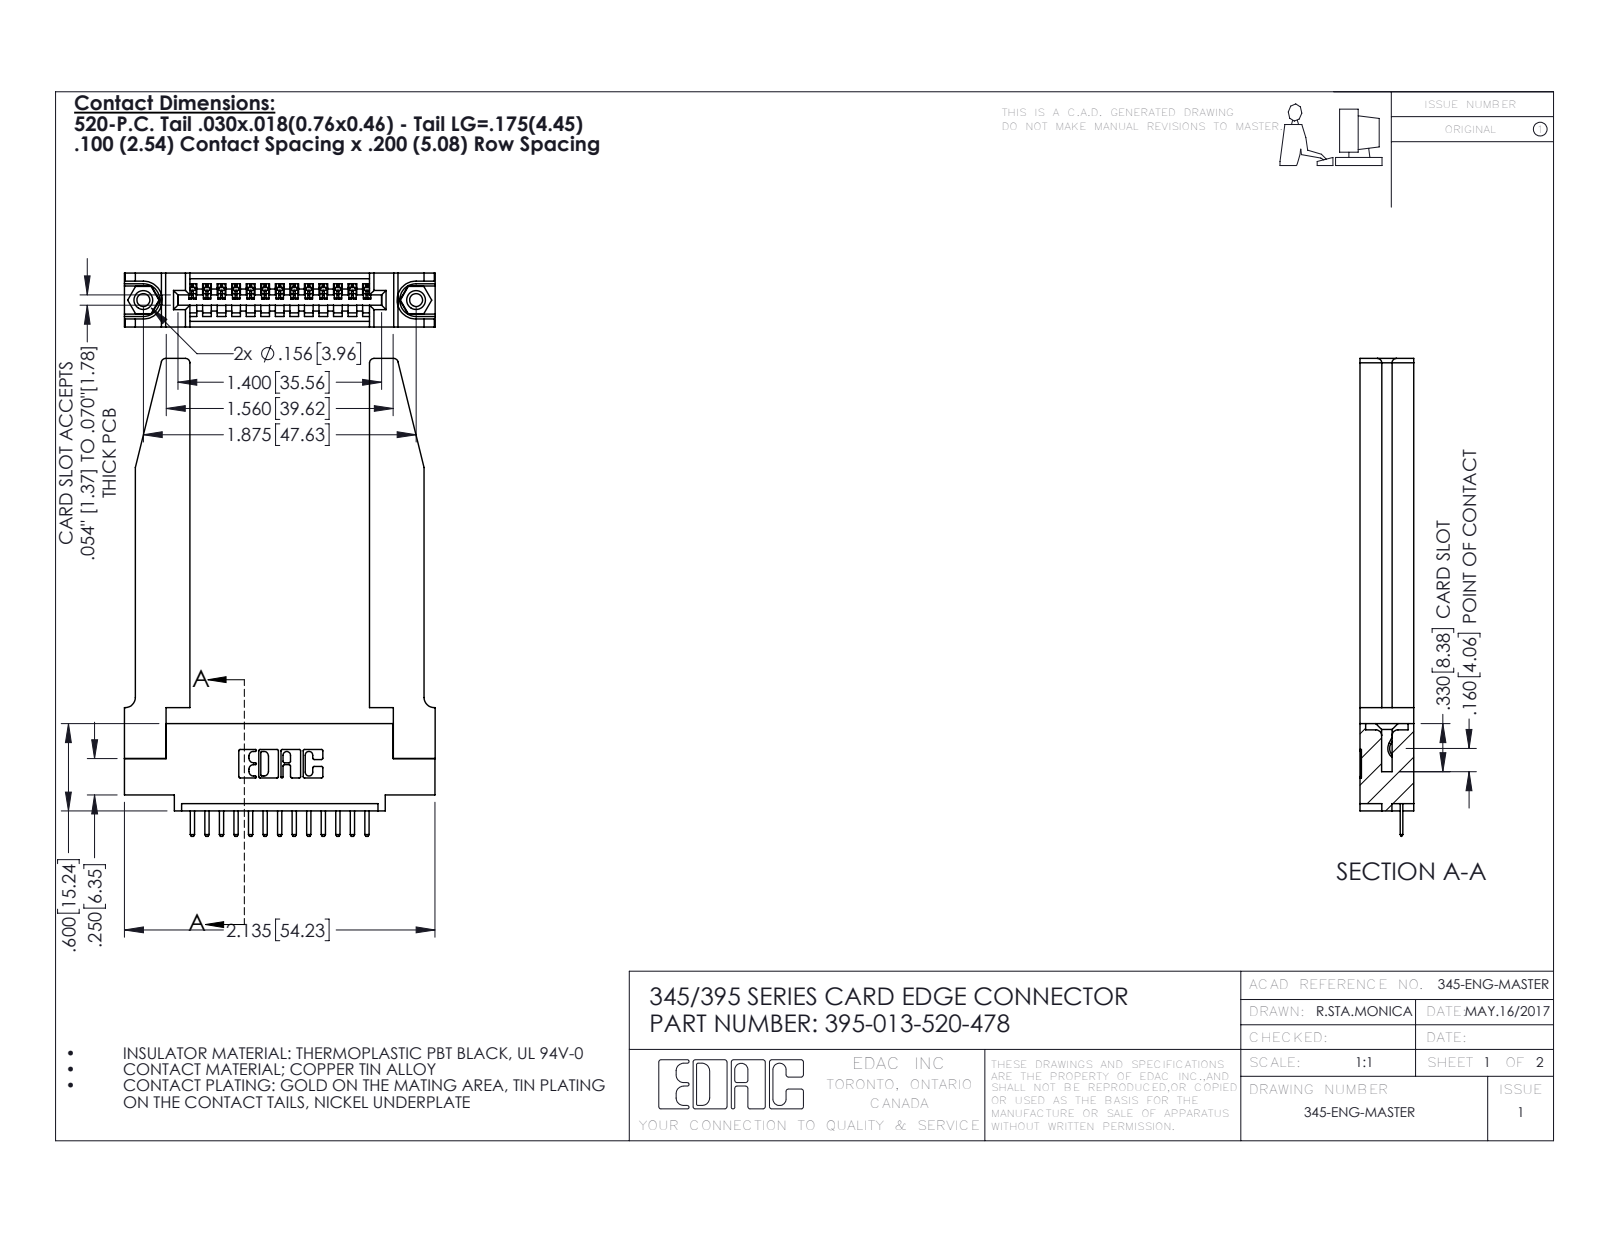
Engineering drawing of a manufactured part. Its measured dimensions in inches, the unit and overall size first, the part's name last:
Units: inches
Overall size (bounding box): 3.285 × 2.136 × 0.37
Round holes (diameter × count): ⌀0.089 ×2, ⌀0.125 ×2, ⌀0.156 ×2, ⌀0.064 ×1
Round bosses / shafts (diameter × count): ⌀0.155 ×2
Partial cylindrical surfaces — rounded edges, fillets, slot ends (radius × count): R0.01 ×28, R0.006 ×26, R0.01 ×22, R0.03 ×8, R0.007 ×6, R0.031 ×6, R0.026 ×3, R0.031 ×2
Main face-to-face distances: 0.37, 0.072, 0.298, 0.148, 0.15, 0.22, 0.077, 1.235, 0.2, 0.098
Hole centre spacings: 0.27, 1.643, 1.875
Volume: 0.767 in³ · Surface area: 19.83 in²
Bodies: 18 solids, 1170 faces (772 planar, 346 cylindrical, 52 other)
Part name (STEP PRODUCT): 395-013-520-478; 345 Part_0.110 Offset - 0.156 Dia-TH; 345-250-001_345-250-001-102; 345-292-001_345-293-120 (+1 more)
STEP written by: SolidWorks 2016 (CONFIG_CONTROL_DESIGN)
